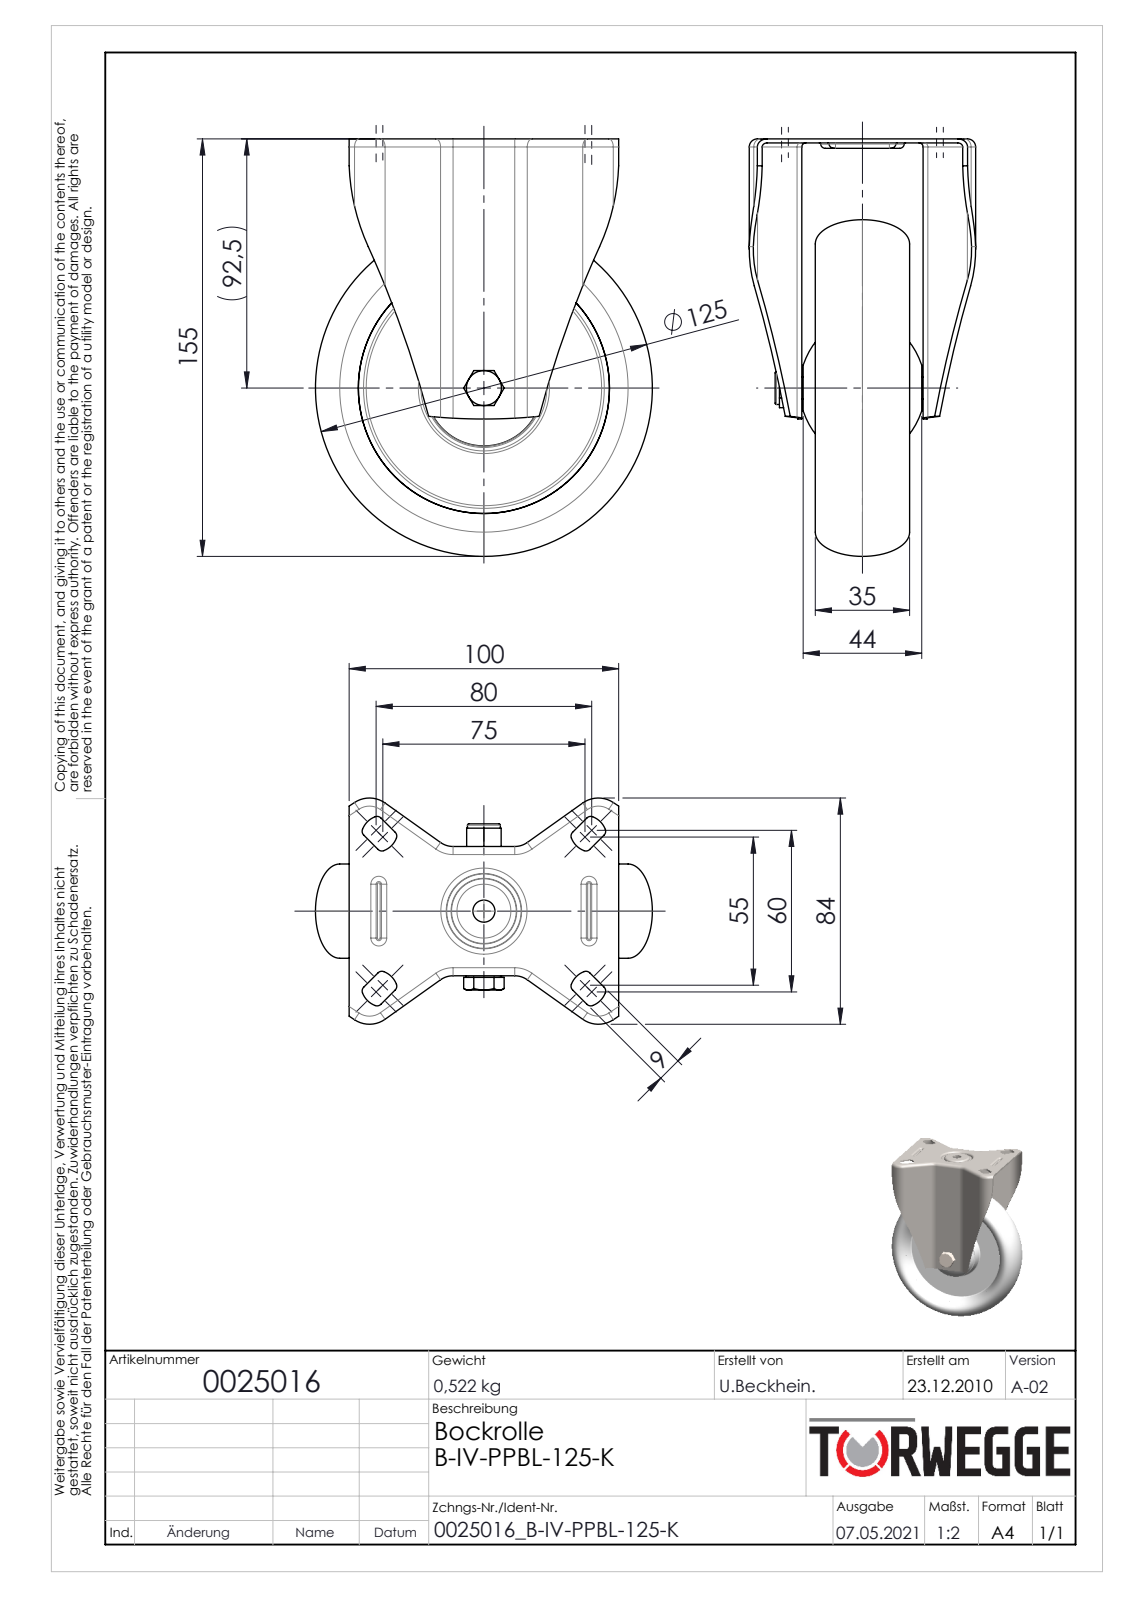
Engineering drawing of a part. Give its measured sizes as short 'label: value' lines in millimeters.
name: 0025016
written by: SolidWorks 2020 (AUTOMOTIVE_DESIGN)
unit: mm
bodies: 8 solids, 386 faces (88 planar, 146 cylindrical, 152 other)
size: 155 × 125 × 84
volume: 277 634 mm³; area: 140 960 mm²
holes: 2× ⌀8.2, 1× ⌀6.65, 1× ⌀8, 1× ⌀29, 1× ⌀33, 1× ⌀35
bosses: 1× ⌀21, 1× ⌀15, 1× ⌀13, 1× ⌀12.2
rounds: 24× R2, 10× R1.5, 10× R3, 8× R0.5, 8× R8.07, 4× R8, 4× R8.5, 4× R9.5
face distances: 1.5, 21.32, 5, 26.5, 21.5, 20, 46.5, 25, 22.82, 19.82
